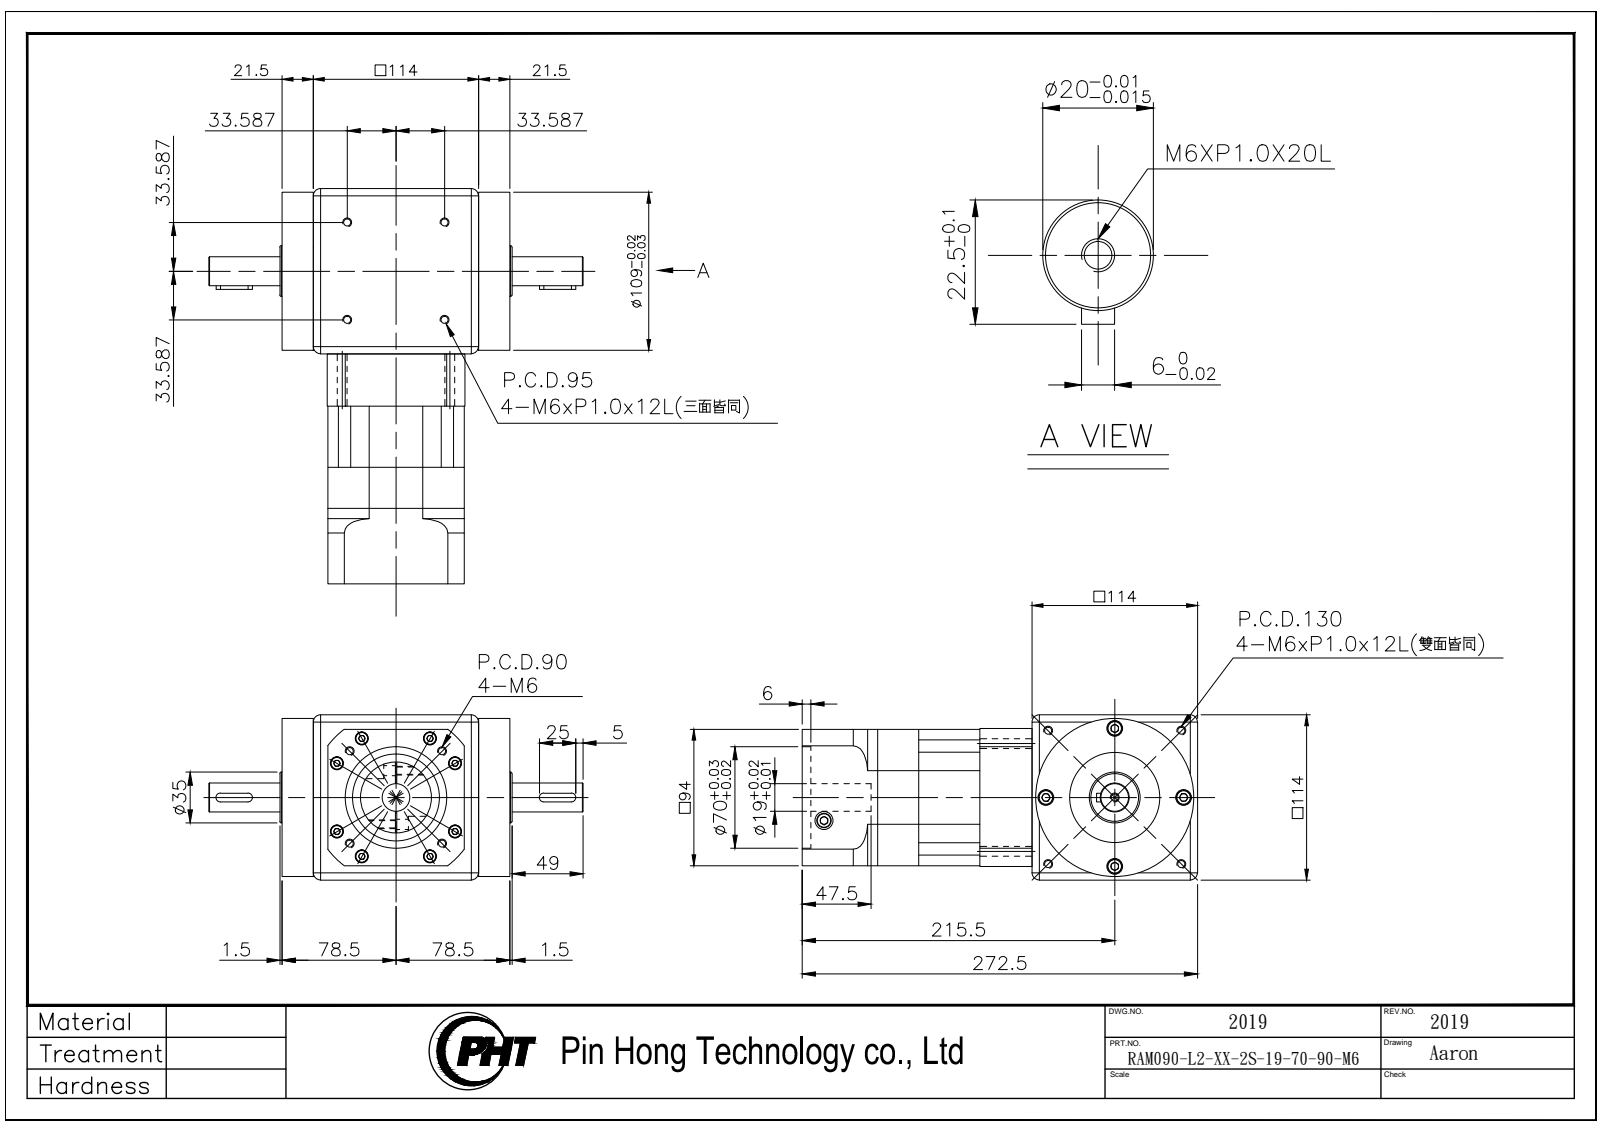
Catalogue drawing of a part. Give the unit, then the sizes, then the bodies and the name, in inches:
Units: inches
Overall size (bounding box): 10.728 × 10.157 × 4.488
Round holes (diameter × count): ⌀0.197 ×17, ⌀0.205 ×8, ⌀0.354 ×8, ⌀0.26 ×4, ⌀0.268 ×4, ⌀0.433 ×4, ⌀0.5 ×2, ⌀0.098 ×1, ⌀0.748 ×1, ⌀2.362 ×1, ⌀2.756 ×1
Round bosses / shafts (diameter × count): ⌀0.394 ×8, ⌀0.335 ×8, ⌀4.291 ×1, ⌀3.15 ×1, ⌀2.441 ×1, ⌀1.929 ×1, ⌀1.378 ×1, ⌀0.787 ×1
Partial cylindrical surfaces — rounded edges, fillets, slot ends (radius × count): R0.118 ×4, R0.236 ×4, R1.988 ×1, R2.323 ×1, R3.114 ×1
Main face-to-face distances: 4.488, 0.394, 4.094, 4.193, 1.114, 3.079, 8.681, 7.567, 3.701, 4.941
Hole centre spacings: 1.85, 2.645, 0.479, 0.486, 0.554, 1.811, 1.87, 2.206
Volume: 188.6 in³ · Surface area: 390.3 in²
Bodies: 4 solids, 682 faces (306 planar, 240 cylindrical, 136 other)
Part name (STEP PRODUCT): RAM090-L2-XX-2S-19-70-90-M6_2019
STEP written by: SolidWorks 2016 (AUTOMOTIVE_DESIGN)
